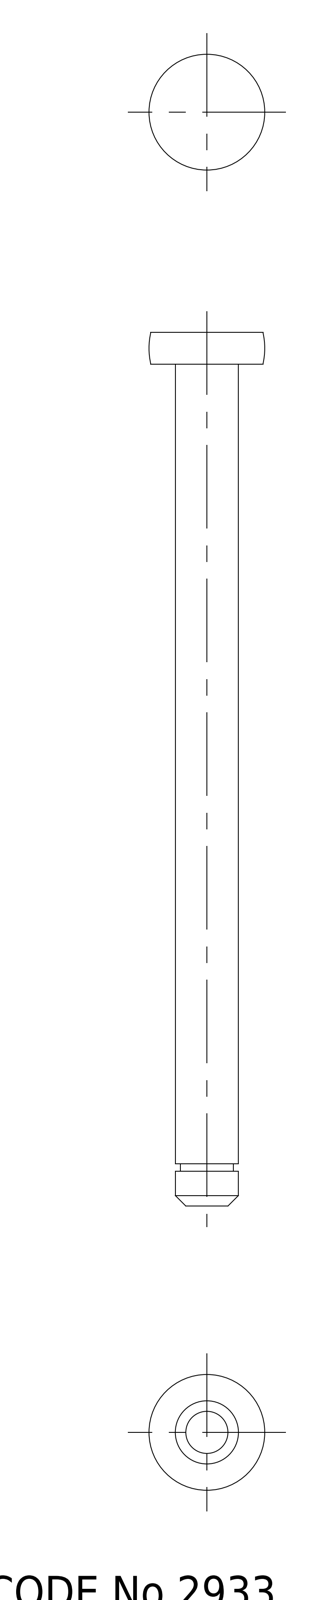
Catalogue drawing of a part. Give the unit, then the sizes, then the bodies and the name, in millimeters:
Units: millimetres
Overall size (bounding box): 83 × 11 × 11
Round bosses / shafts (diameter × count): ⌀6 ×1, ⌀5 ×1
Main face-to-face distances: 3, 80, 83, 4, 76, 79, 3.3, 0.7, 76.7, 79.7
Volume: 2 527 mm³ · Surface area: 1 793 mm²
Bodies: 1 solid, 15 faces (5 planar, 6 cylindrical, 4 other)
Part name (STEP PRODUCT): shaft; TH_121_6_80
STEP written by: SolidWorks 2015 (AUTOMOTIVE_DESIGN)
